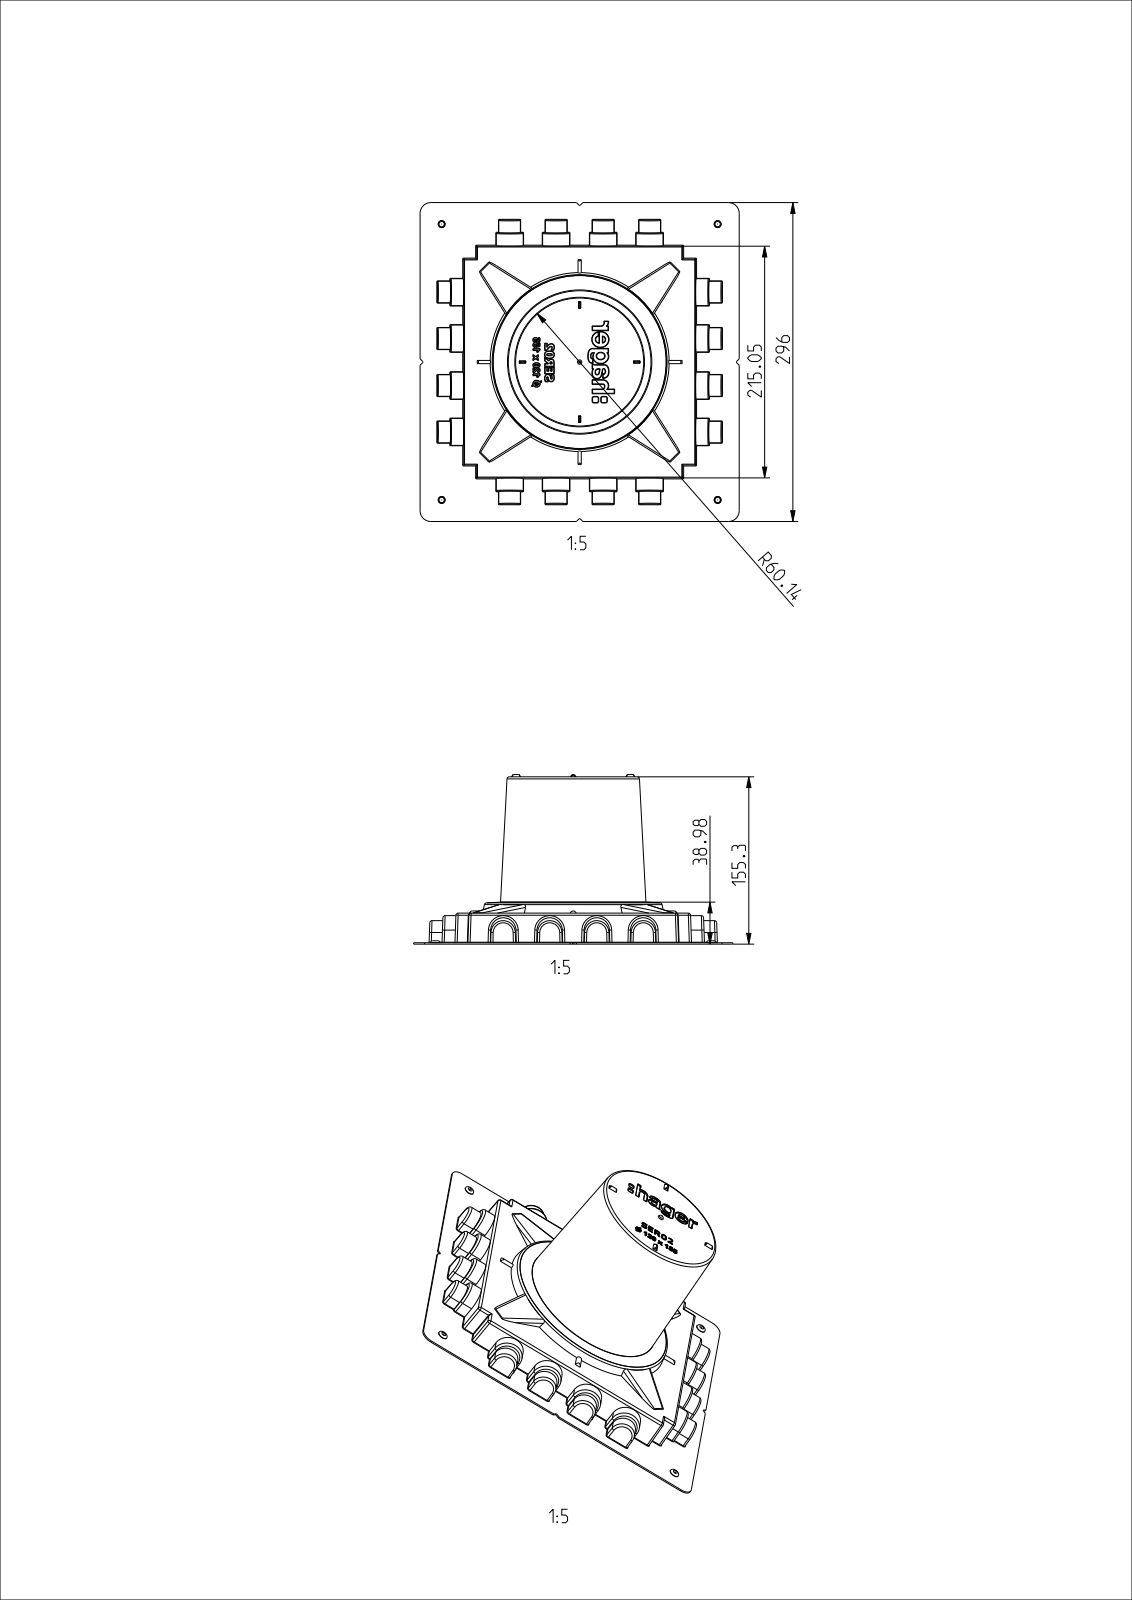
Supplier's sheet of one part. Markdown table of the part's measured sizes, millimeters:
| quantity | value |
| --- | --- |
| part name | T-00107 |
| STEP written by | CREO PARAMETRIC BY PTC INC, 2022281 (AUTOMOTIVE_DESIGN) |
| units | millimeters |
| bodies | 1 solid, 2742 faces (629 planar, 805 cylindrical, 1308 other) |
| overall size | 296 × 296 × 157.47 |
| volume | 222 190 mm³ |
| surface area | 343 832 mm² |
| round holes (diameter × count) | 0.2 × 4 |
| partial cylindrical surfaces (radius × count) | 0.15 × 88, 0.3 × 80, 0.75 × 80, 2.05 × 80, 0.45 × 53, 0.5 × 52, 0.1 × 34, 0.2 × 25 |
| main face-to-face distances | 1.3, 27.5, 154, 126.5, 26.2, 28.8, 23.98, 11.99, 155.3, 127.8 |
| hole center spacings | 256, 362.04 |
